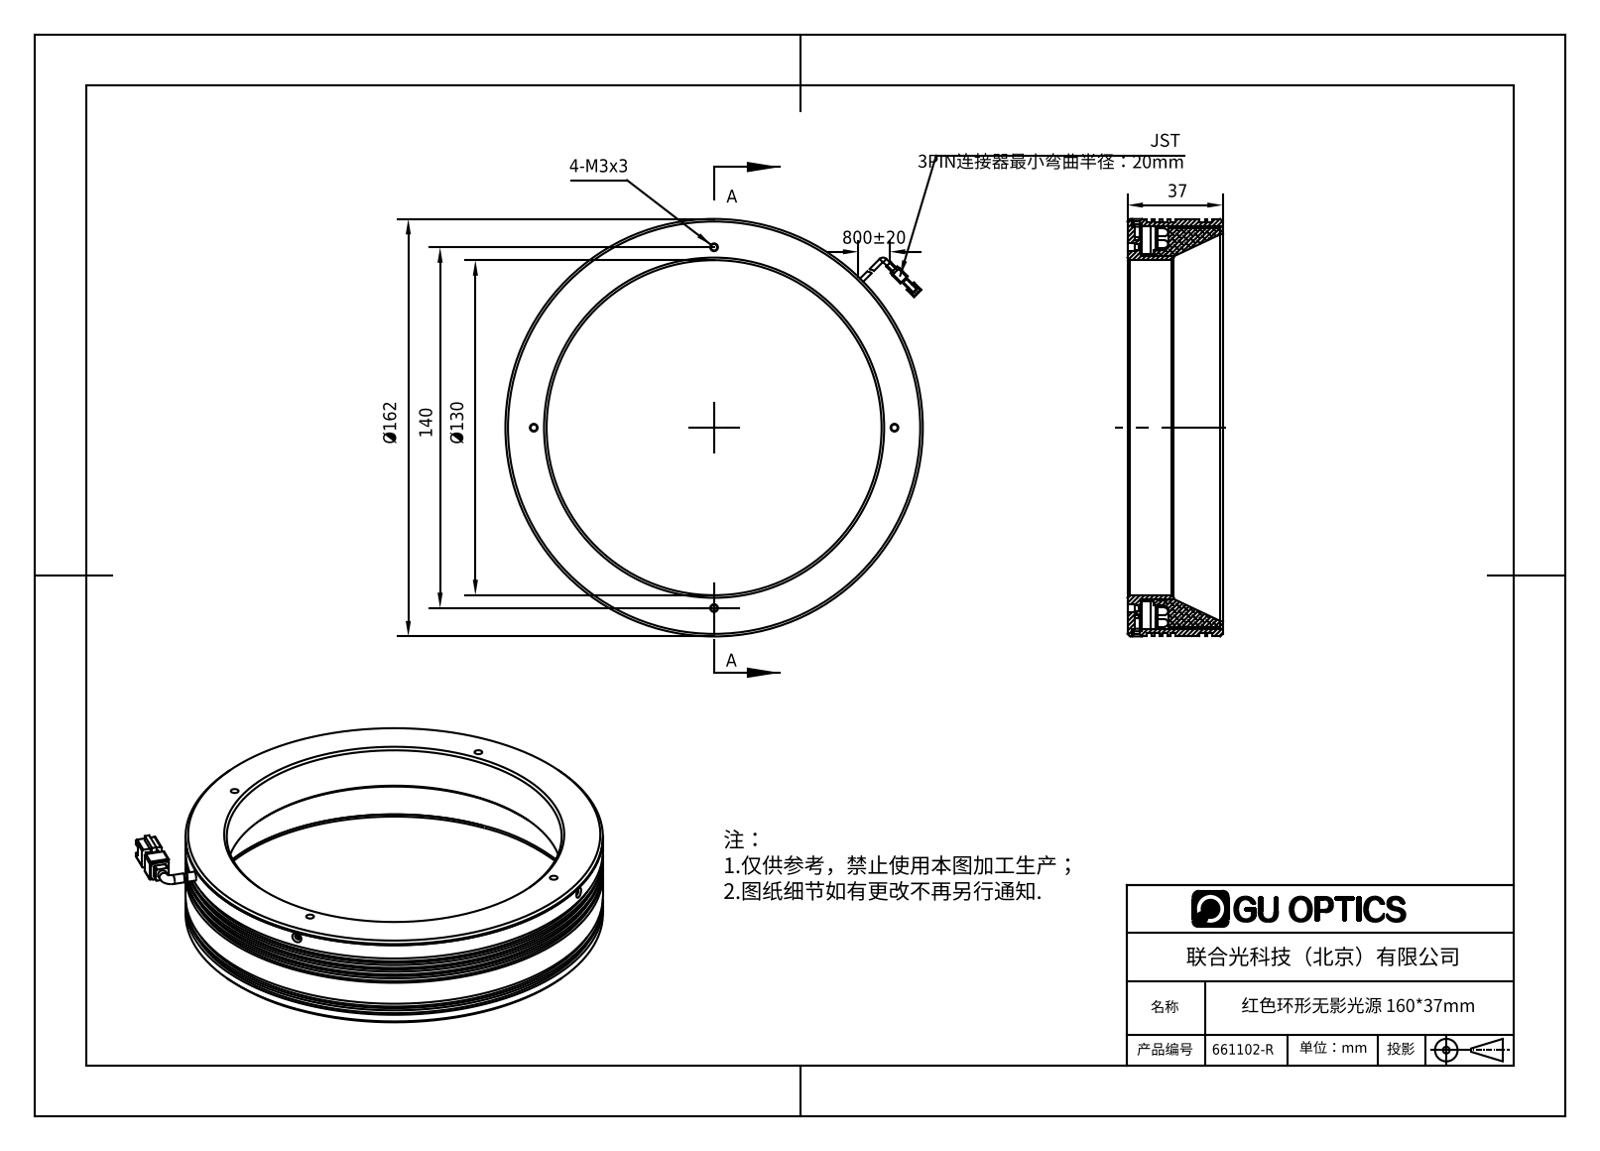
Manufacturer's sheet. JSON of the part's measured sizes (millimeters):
{"part_name": "661102", "step_written_by": "SolidWorks 2016 (AUTOMOTIVE_DESIGN)", "units": "millimeters", "bodies": {"solids": 5, "faces": 260, "planar": 91, "cylindrical": 129, "other": 40}, "overall_size": [168.11, 162, 38.5], "volume_mm3": 159756, "surface_area_mm2": 113568, "round_holes": [[2.5, 4], [3, 4], [1.6, 2], [2, 2], [2.4, 2], [130, 1], [133, 1], [150, 1], [158, 1]], "round_bosses_or_shafts": [[3.5, 2], [162, 1], [159.6, 1], [156, 1], [155, 1], [138, 1], [135, 1]], "partial_cylinders_radius": [[0.5, 8], [1, 4], [6, 1]], "face_to_face_distances": [5, 3, 14.5, 6, 1, 11, 2, 3.5, 20.5, 20], "hole_center_spacings": [70, 98.99, 140]}
